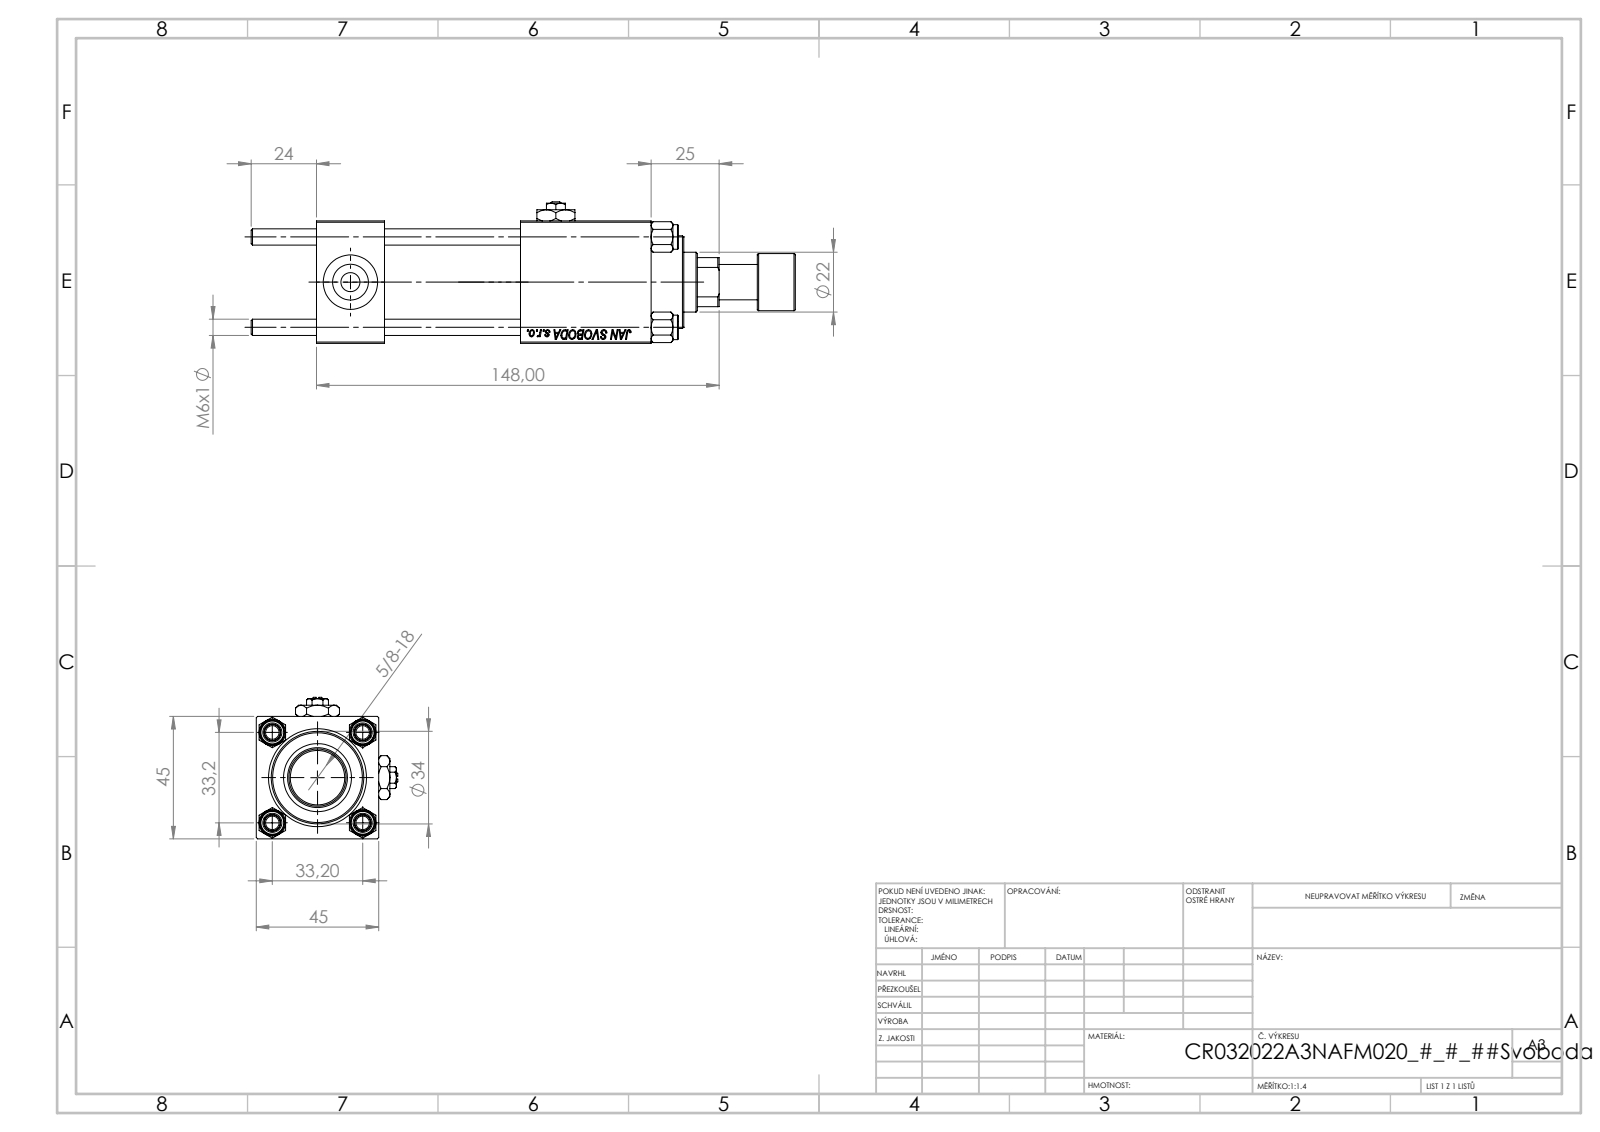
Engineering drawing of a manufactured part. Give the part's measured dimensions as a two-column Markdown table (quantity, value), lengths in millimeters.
| quantity | value |
| --- | --- |
| part name | Zatka_pro_OIL_PORT; NUT_M5; CR025_012_A_0_G_A_G_M_020_+#_##_TYCINKA; V215CR_BODY_A (+3 more) |
| STEP written by | SolidWorks 2019 (CONFIG_CONTROL_DESIGN) |
| units | millimeters |
| bodies | 14 solids, 1243 faces (567 planar, 94 cylindrical, 582 other) |
| overall size | 200 × 52 × 52 |
| volume | 219 050 mm³ |
| surface area | 81 094 mm² |
| round holes (diameter × count) | 6 × 4, 7 × 2, 13.16 × 2, 20 × 2, 10.5 × 1, 13 × 1, 22 × 1, 24 × 1, 25 × 1, 32 × 1, 33 × 1 |
| round bosses / shafts (diameter × count) | 9 × 4, 38 × 1, 34 × 1, 21 × 1, 13 × 1 |
| main face-to-face distances | 45, 25, 123, 50, 75, 98, 48, 44.8, 94.3, 69.3 |
| hole center spacings | 23.48, 33.2, 46.95 |
